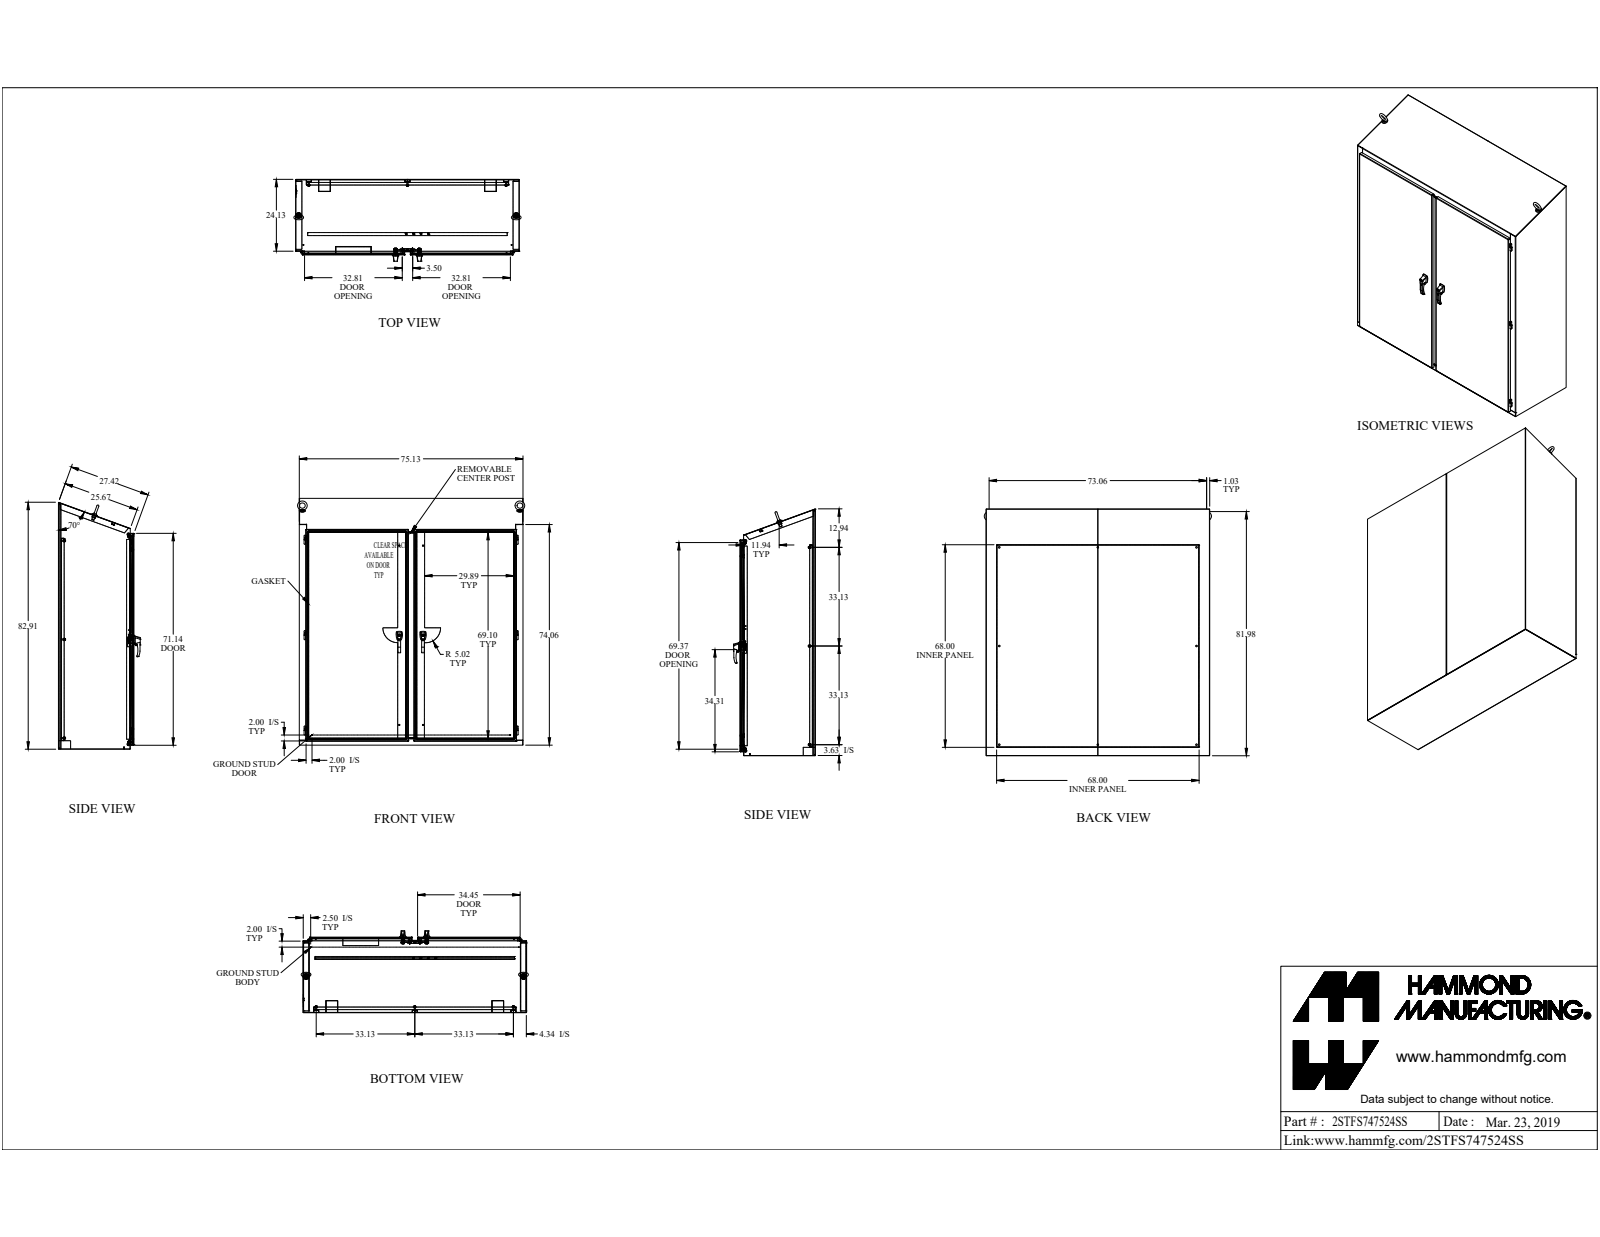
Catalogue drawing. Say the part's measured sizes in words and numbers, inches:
The part is named "2STFS747524SS". Its 3-D file was written by "SolidWorks 2019 (CONFIG_CONTROL_DESIGN)". It is 146 solids with 2404 faces: 1417 planar, 729 cylindrical and 258 other. Overall it measures 82.86 by 76.307 by 27.491 inches. Its volume is 2 823 cubic inches and its surface area 56 392 square inches. Round holes: 8 of diameter 0.307, 8 of diameter 0.35, 8 of diameter 0.563, 7 of diameter 0.25, 6 of diameter 0.281, 6 of diameter 0.313, 6 of diameter 0.445, 4 of diameter 0.196, 4 of diameter 0.257, 4 of diameter 0.28, 4 of diameter 0.39, 4 of diameter 0.413. Round bosses or shafts: 12 of diameter 1, 8 of diameter 0.65, 8 of diameter 0.375, 8 of diameter 0.332, 4 of diameter 0.75, 4 of diameter 0.63, 4 of diameter 0.625, 4 of diameter 0.44. Partial cylindrical surfaces (rounded edges, fillets, slot ends): 47 of radius 0.125, 33 of radius 0.5, 32 of radius 0.018, 30 of radius 0.048, 30 of radius 0.143, 20 of radius 0.06, 16 of radius 0.25, 12 of radius 0.03. The main face-to-face distances are 0.095, 0.095, 25.185, 25.28, 25.281, 25.376, 0.125, 23.469, 23.373, 1.812. The hole center spacings are 73.059, 7.983, 74.07, 66.25, 1.126, 1.287, 7.443, 8.062.
